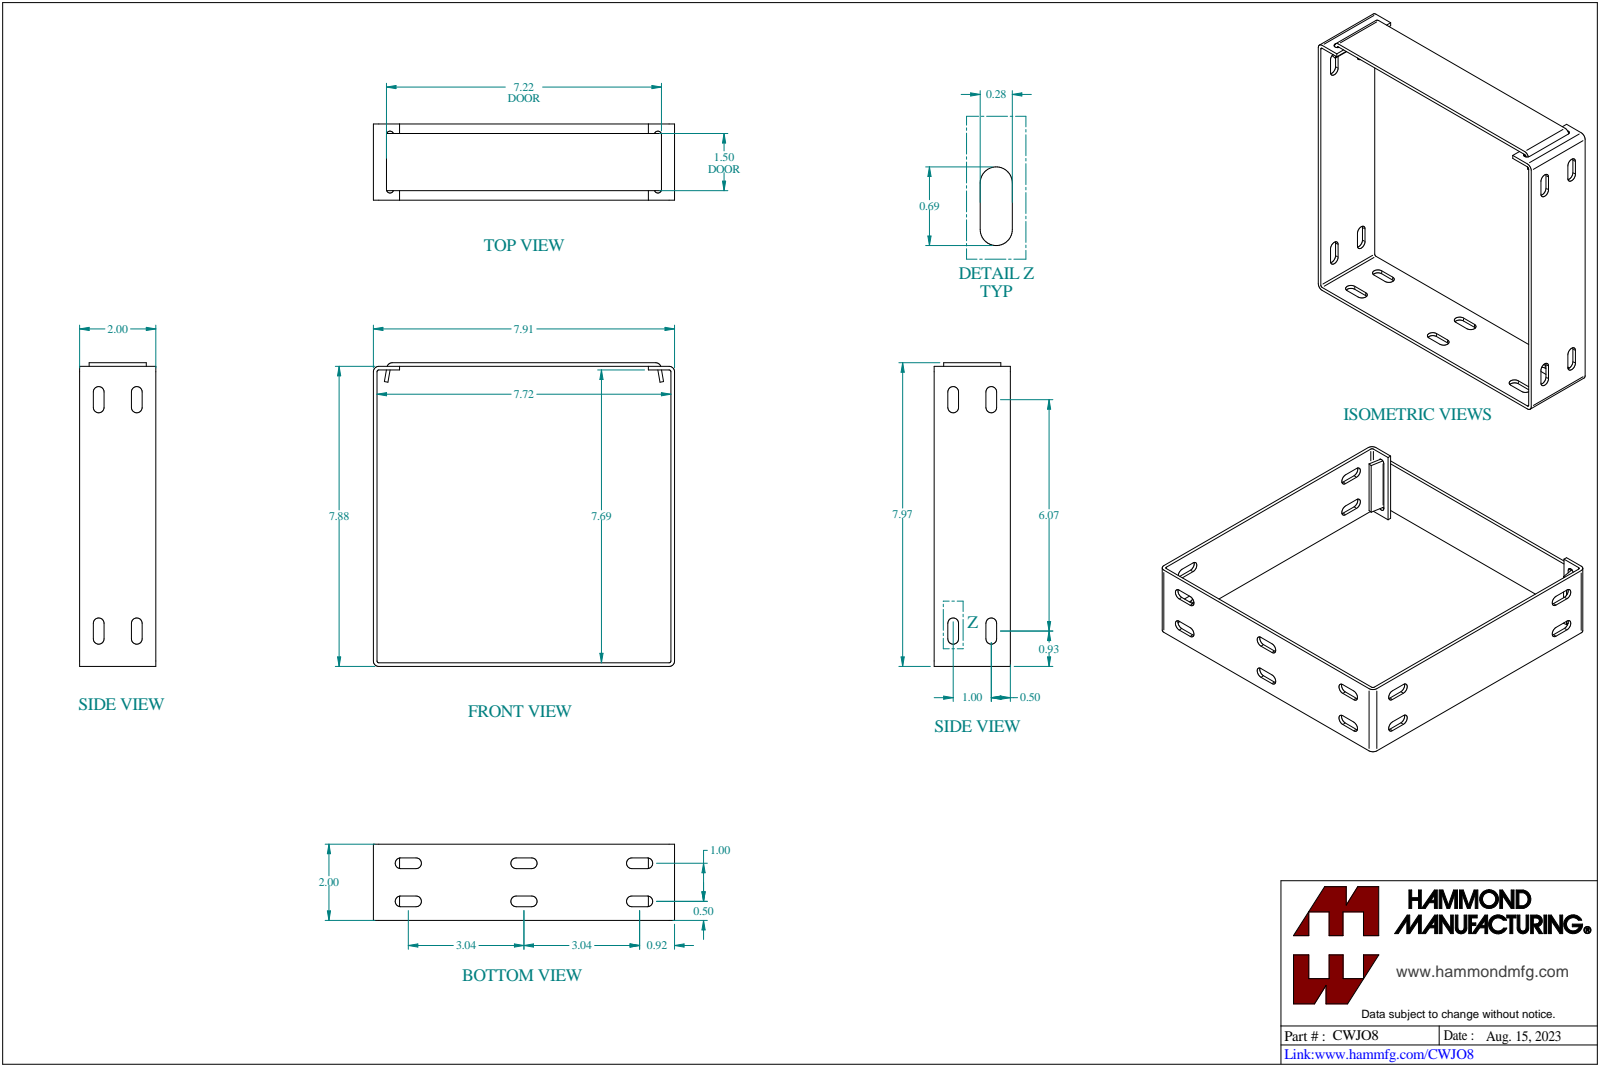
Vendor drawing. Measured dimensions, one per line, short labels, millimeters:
name: CWJO8
written by: SolidWorks 2023 (CONFIG_CONTROL_DESIGN)
unit: mm
bodies: 2 solids, 114 faces (56 planar, 58 cylindrical, 0 other)
size: 202.4 × 200.8 × 50.8
volume: 90 030 mm³; area: 80 900 mm²
rounds: 16× R3.6, 6× R1.2, 6× R3.6, 4× R2.4, 4× R3.6
face distances: 2.4, 198.4, 2.4, 200.8, 196, 197.6, 200, 200, 202.4, 50.8
